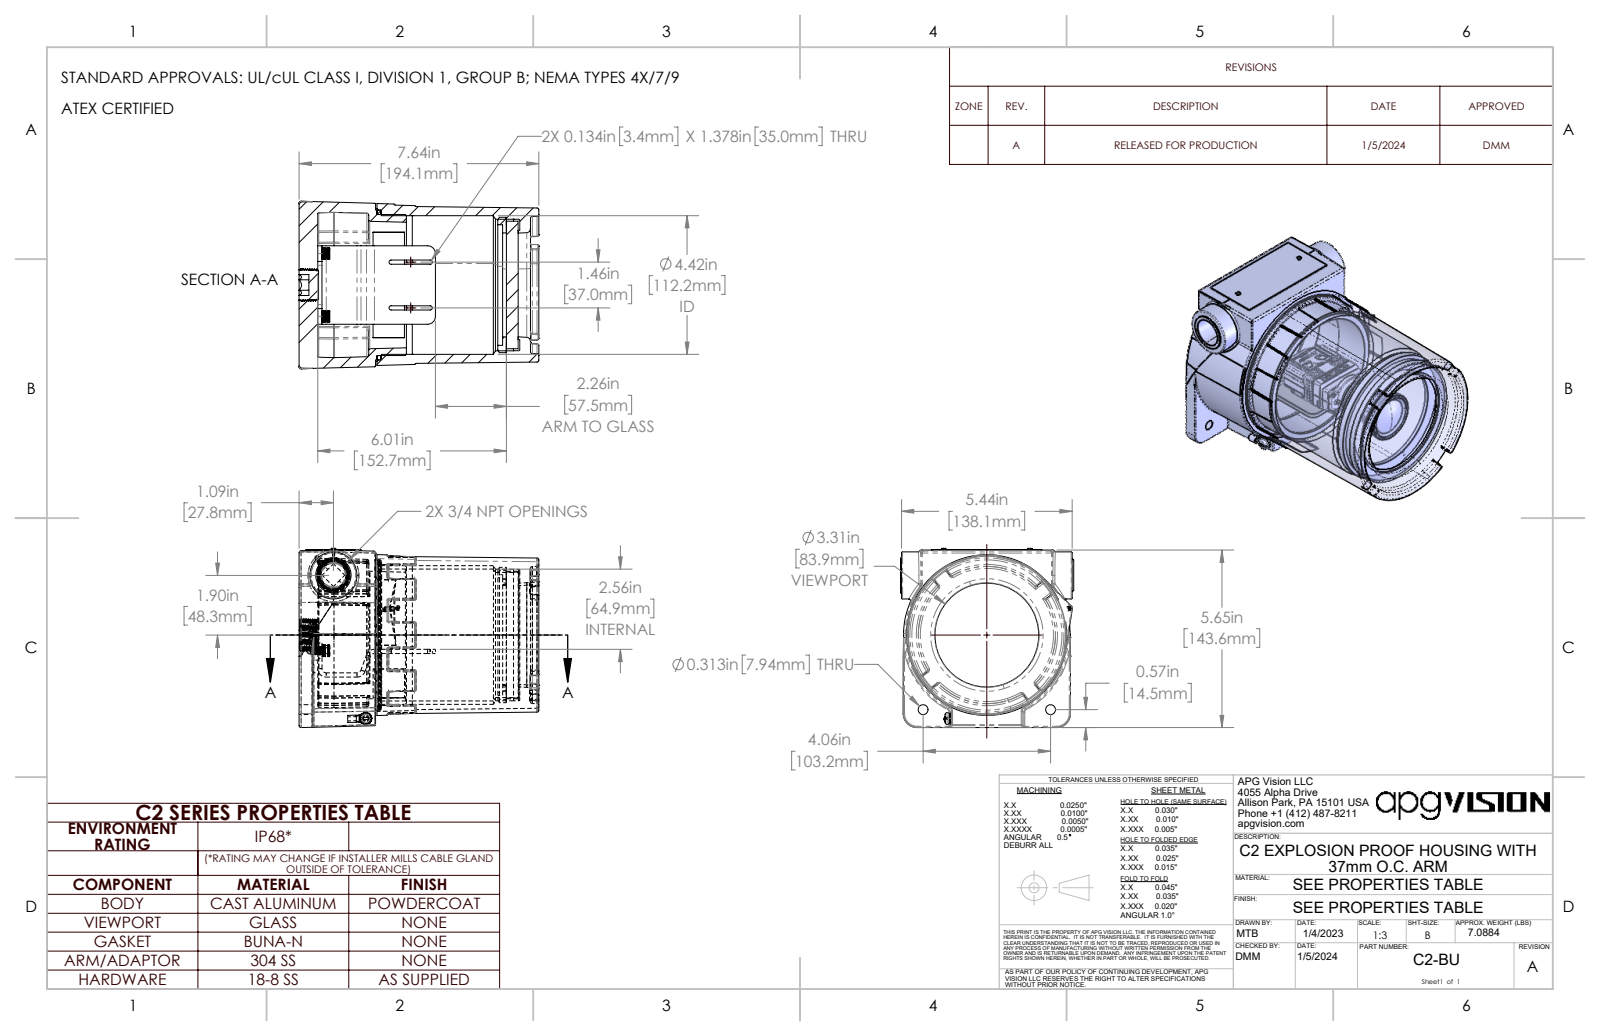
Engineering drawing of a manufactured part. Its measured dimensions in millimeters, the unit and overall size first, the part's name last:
Units: millimetres
Overall size (bounding box): 194.1 × 145 × 140.2
Round holes (diameter × count): ⌀1.7 ×2, ⌀2.4 ×2, ⌀3.7 ×2, ⌀4.8 ×2, ⌀5.1 ×2, ⌀6.8 ×2, ⌀8 ×2, ⌀10.2 ×2, ⌀2.7 ×1, ⌀3.3 ×1, ⌀5 ×1, ⌀5 ×1
Round bosses / shafts (diameter × count): ⌀6.4 ×2, ⌀4.8 ×2, ⌀4.7 ×2, ⌀1.9 ×2, ⌀121.2 ×1, ⌀114.1 ×1, ⌀109.5 ×1, ⌀103.2 ×1
Partial cylindrical surfaces — rounded edges, fillets, slot ends (radius × count): R0.8 ×19, R0.8 ×11, R1.6 ×5, R1.6 ×5, R1.7 ×4, R6.4 ×4, R0.6 ×3, R1.6 ×3
Main face-to-face distances: 15.1, 177.3, 162.3, 167.8, 152.7, 9.5, 3.4, 0.5, 19.1, 61.9
Hole centre spacings: 28.4, 18, 40.2, 45.2, 52.3, 54.4, 73.2, 79.4
Volume: 1 094 000 mm³ · Surface area: 301 800 mm²
Bodies: 20 solids, 1575 faces (461 planar, 260 cylindrical, 854 other)
Part name (STEP PRODUCT): 4638K515_4638K515; 92196A535_92196A535; 201109; C2-BU (+1 more)
STEP written by: SolidWorks 2022 (CONFIG_CONTROL_DESIGN)
